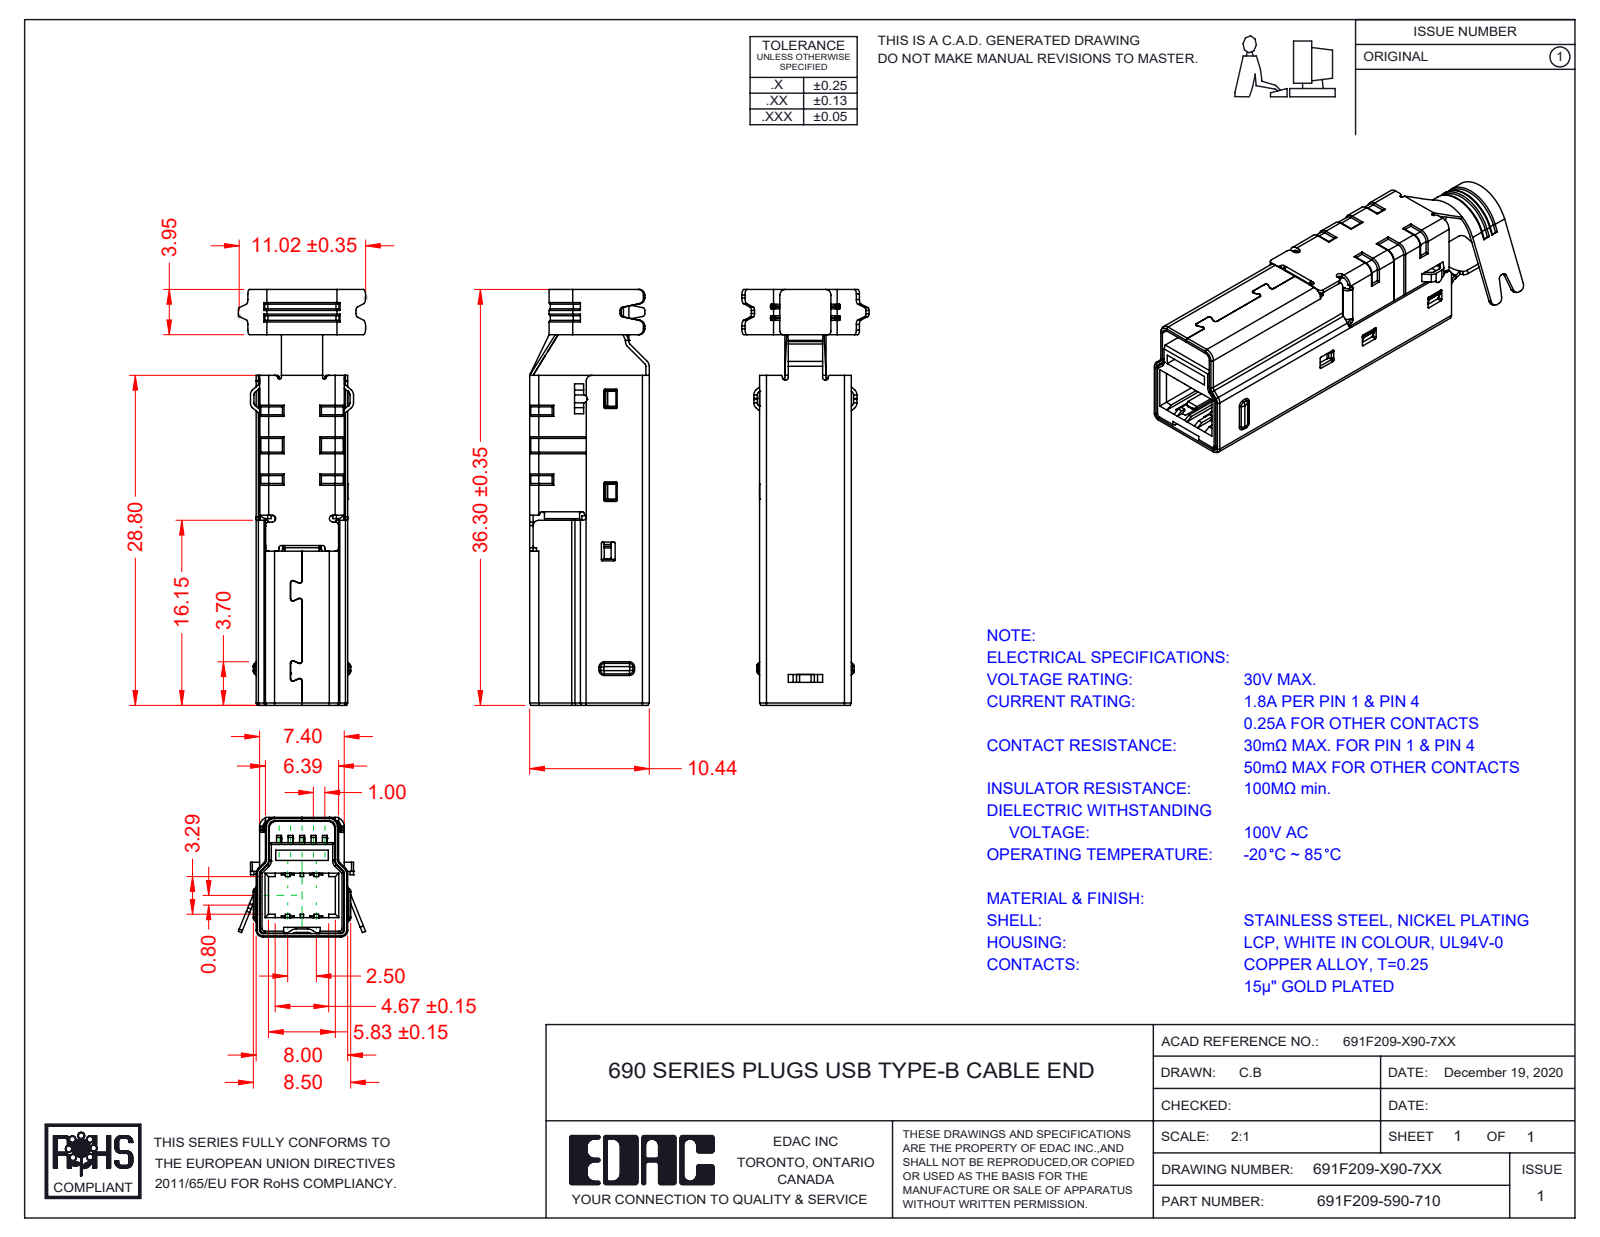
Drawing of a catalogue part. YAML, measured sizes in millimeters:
part_name: "Insulator 691F209-X90-7XX_White; Shell 1 691F209-X90-7XX; Shell 2 691F209-X90-7XX; Contacts 691F209-X90-7XX (+1 more)"
step_written_by: "SolidWorks 2020 (AUTOMOTIVE_DESIGN)"
units: millimeters
bodies: {solids: 12, faces: 1476, planar: 812, cylindrical: 525, other: 139}
overall_size: [36.3, 11.11, 10.44]
volume: 931
surface_area: 3750
partial_cylinders:
  - {radius: 0.15, count: 130}
  - {radius: 0.1, count: 56}
  - {radius: 0.3, count: 44}
  - {radius: 0.2, count: 29}
  - {radius: 0.5, count: 22}
  - {radius: 0.6, count: 12}
  - {radius: 0.4, count: 10}
  - {radius: 0.2, count: 8}
face_to_face_distances: [7.4, 10.14, 7.7, 0.6, 7.1, 9.84, 0.81, 10.44, 8, 0.34]
